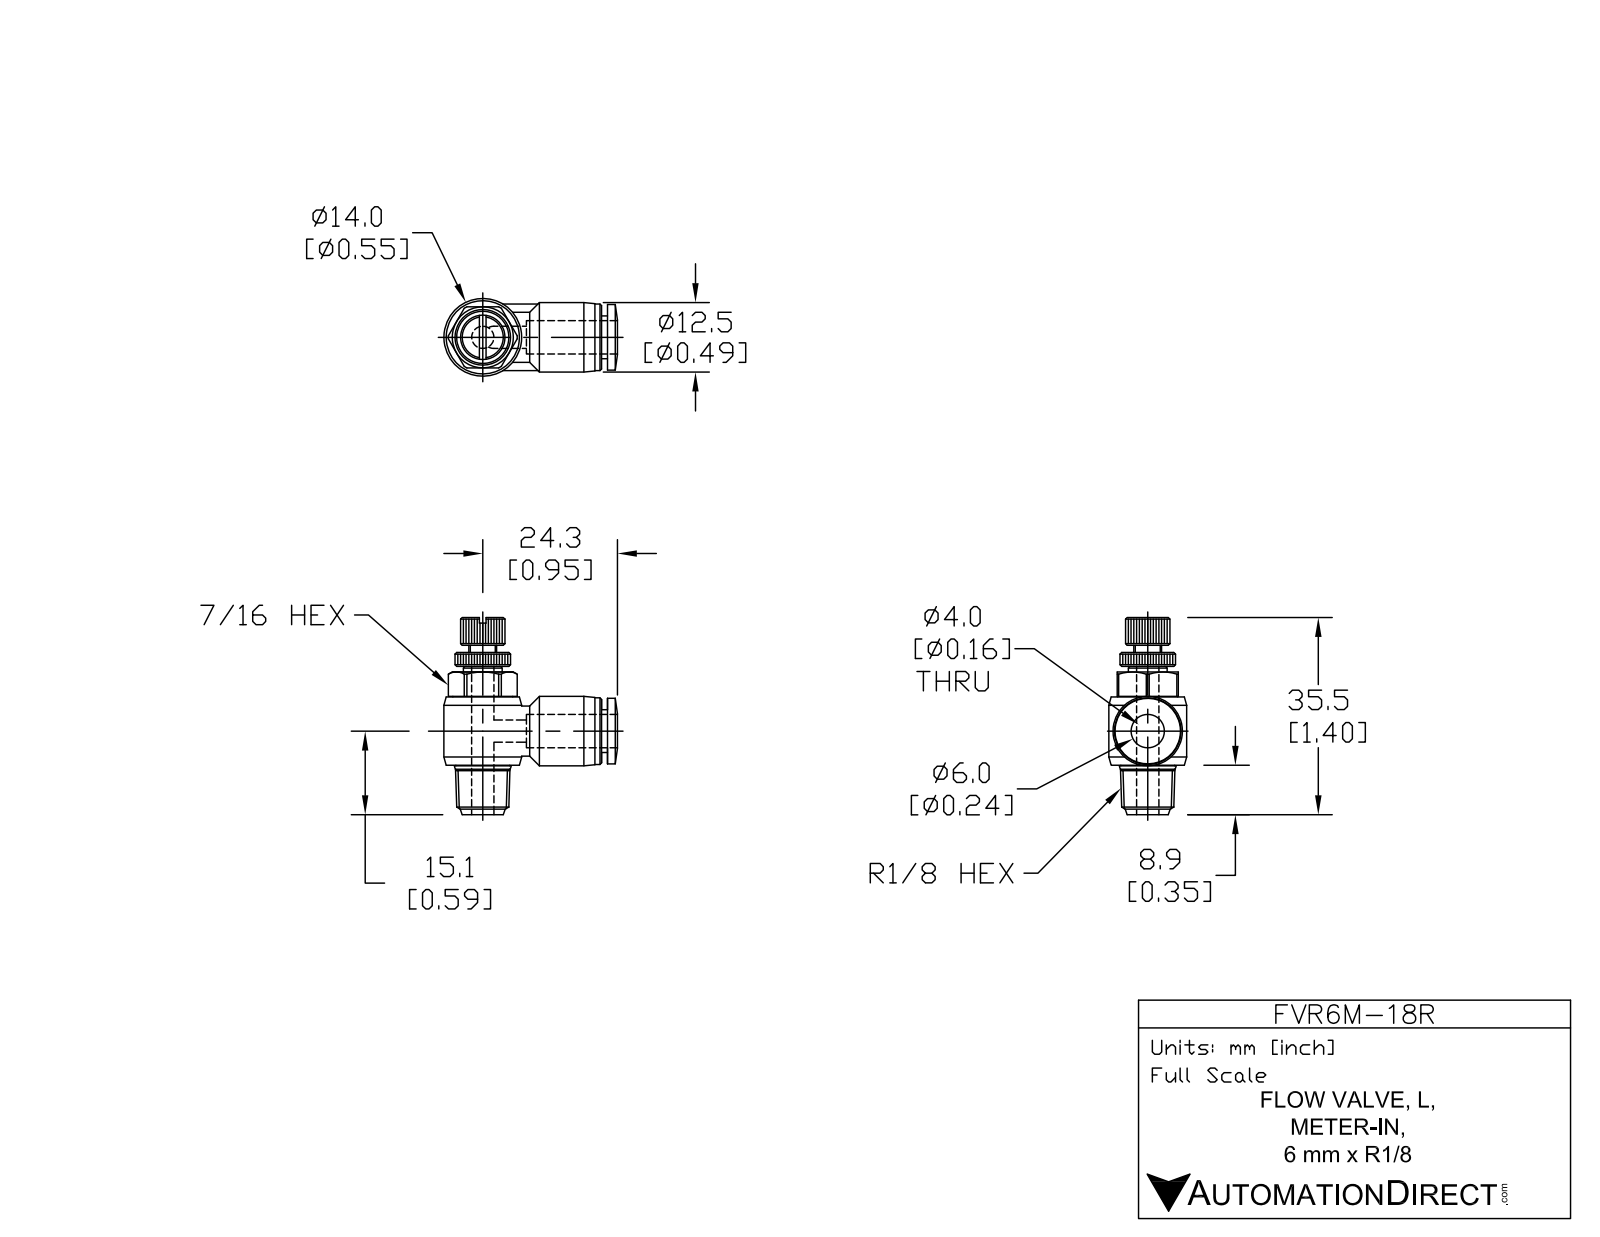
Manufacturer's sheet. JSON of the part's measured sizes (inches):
{"part_name": "FVR6M-18R", "step_written_by": "SolidWorks 2015 (AUTOMOTIVE_DESIGN)", "units": "inches", "bodies": {"solids": 1, "faces": 492, "planar": 189, "cylindrical": 113, "other": 190}, "overall_size": [1.602, 1.23, 0.551], "volume_in3": 0.29, "surface_area_in2": 4.897, "round_holes": [[0.118, 2], [0.248, 1]], "round_bosses_or_shafts": [[0.551, 1], [0.492, 1], [0.472, 1], [0.465, 1], [0.425, 1], [0.382, 1], [0.354, 1], [0.303, 1]], "partial_cylinders_radius": [[0.157, 1], [0.197, 1], [0.244, 1]], "face_to_face_distances": [0.433, 0.453, 0.661, 0.041, 0.206, 0.799, 0.138, 0.039, 0.484, 0.177]}
